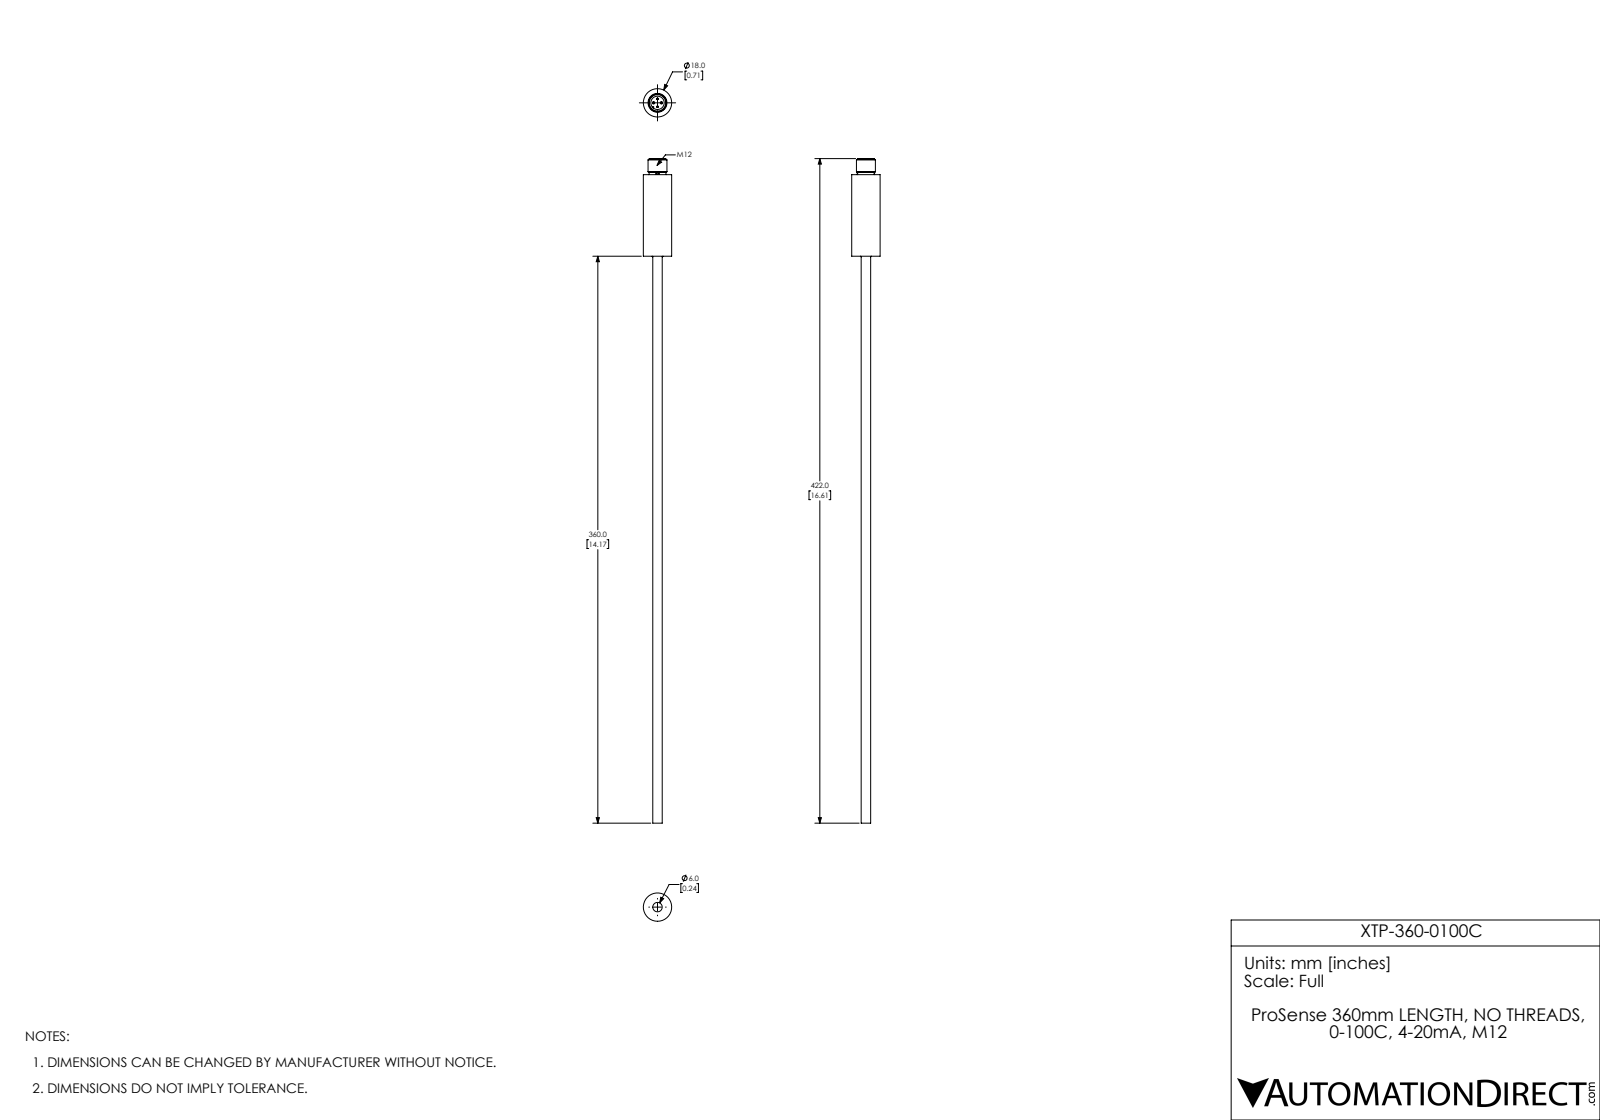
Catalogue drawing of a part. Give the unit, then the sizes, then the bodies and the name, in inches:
Units: inches
Overall size (bounding box): 16.614 × 0.709 × 0.709
Round holes (diameter × count): ⌀0.335 ×1
Round bosses / shafts (diameter × count): ⌀0.04 ×4, ⌀0.709 ×1, ⌀0.472 ×1, ⌀0.421 ×1, ⌀0.413 ×1, ⌀0.236 ×1
Partial cylindrical surfaces — rounded edges, fillets, slot ends (radius × count): R0.016 ×1
Main face-to-face distances: 2.039, 2.087, 0.047, 2.441, 0.402, 0.354, 14.173, 16.213, 16.26, 16.614
Volume: 1.463 in³ · Surface area: 16.93 in²
Bodies: 1 solid, 67 faces (24 planar, 21 cylindrical, 22 other)
Part name (STEP PRODUCT): XTP-360-0100C
STEP written by: SolidWorks 2017 (AUTOMOTIVE_DESIGN)
